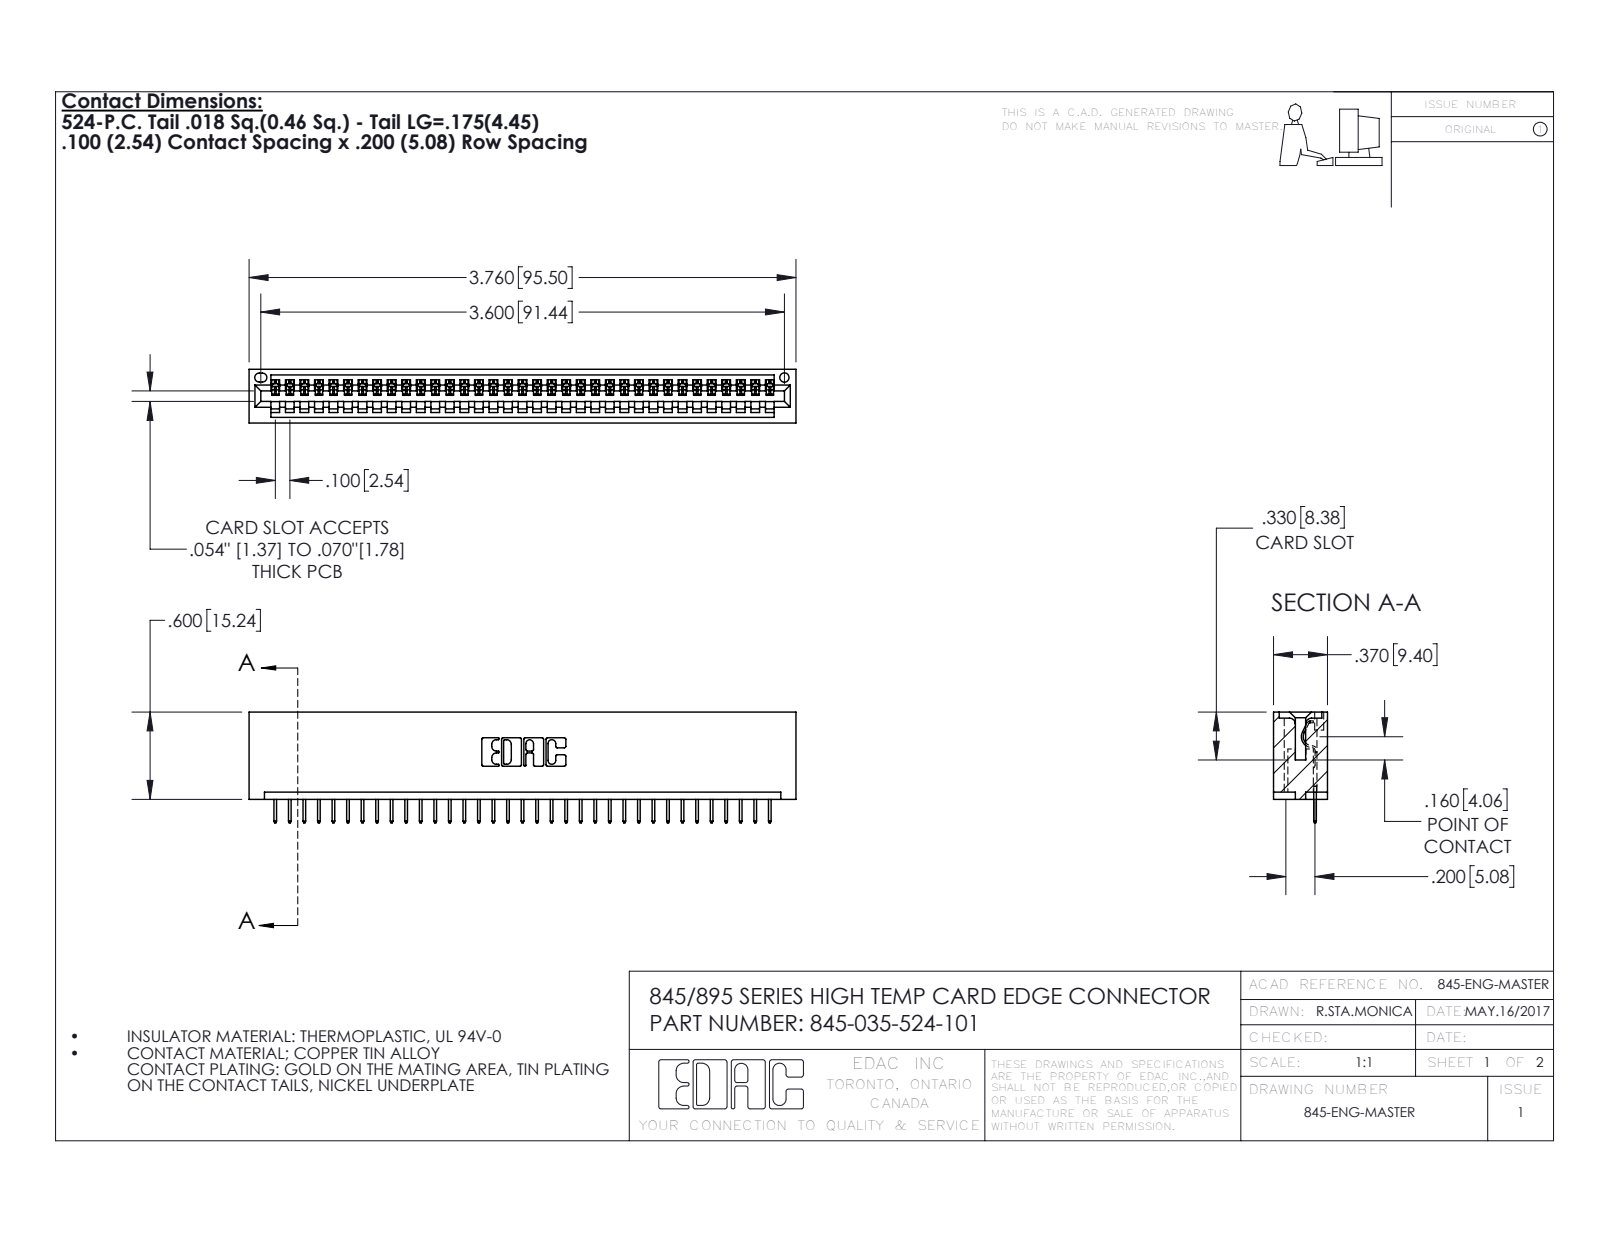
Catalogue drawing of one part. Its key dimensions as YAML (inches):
part_name: "345 Part_No Mounting Lugs; 345-292-001_345-293-124; 345-035-524-101"
step_written_by: "SolidWorks 2016 (CONFIG_CONTROL_DESIGN)"
units: inches
bodies: {solids: 36, faces: 2288, planar: 1686, cylindrical: 602, other: 0}
overall_size: [3.76, 0.762, 0.37]
volume: 0.577
surface_area: 18.95
round_holes:
  - {diameter: 0.064, count: 1}
partial_cylinders:
  - {radius: 0.006, count: 70}
  - {radius: 0.01, count: 22}
  - {radius: 0.007, count: 6}
  - {radius: 0.031, count: 6}
  - {radius: 0.026, count: 3}
  - {radius: 0.031, count: 2}
  - {radius: 0.04, count: 2}
  - {radius: 0.014, count: 1}
face_to_face_distances: [0.298, 0.072, 0.37, 0.2, 0.098, 0.272, 0.025, 0.225, 0.072, 0.149]
